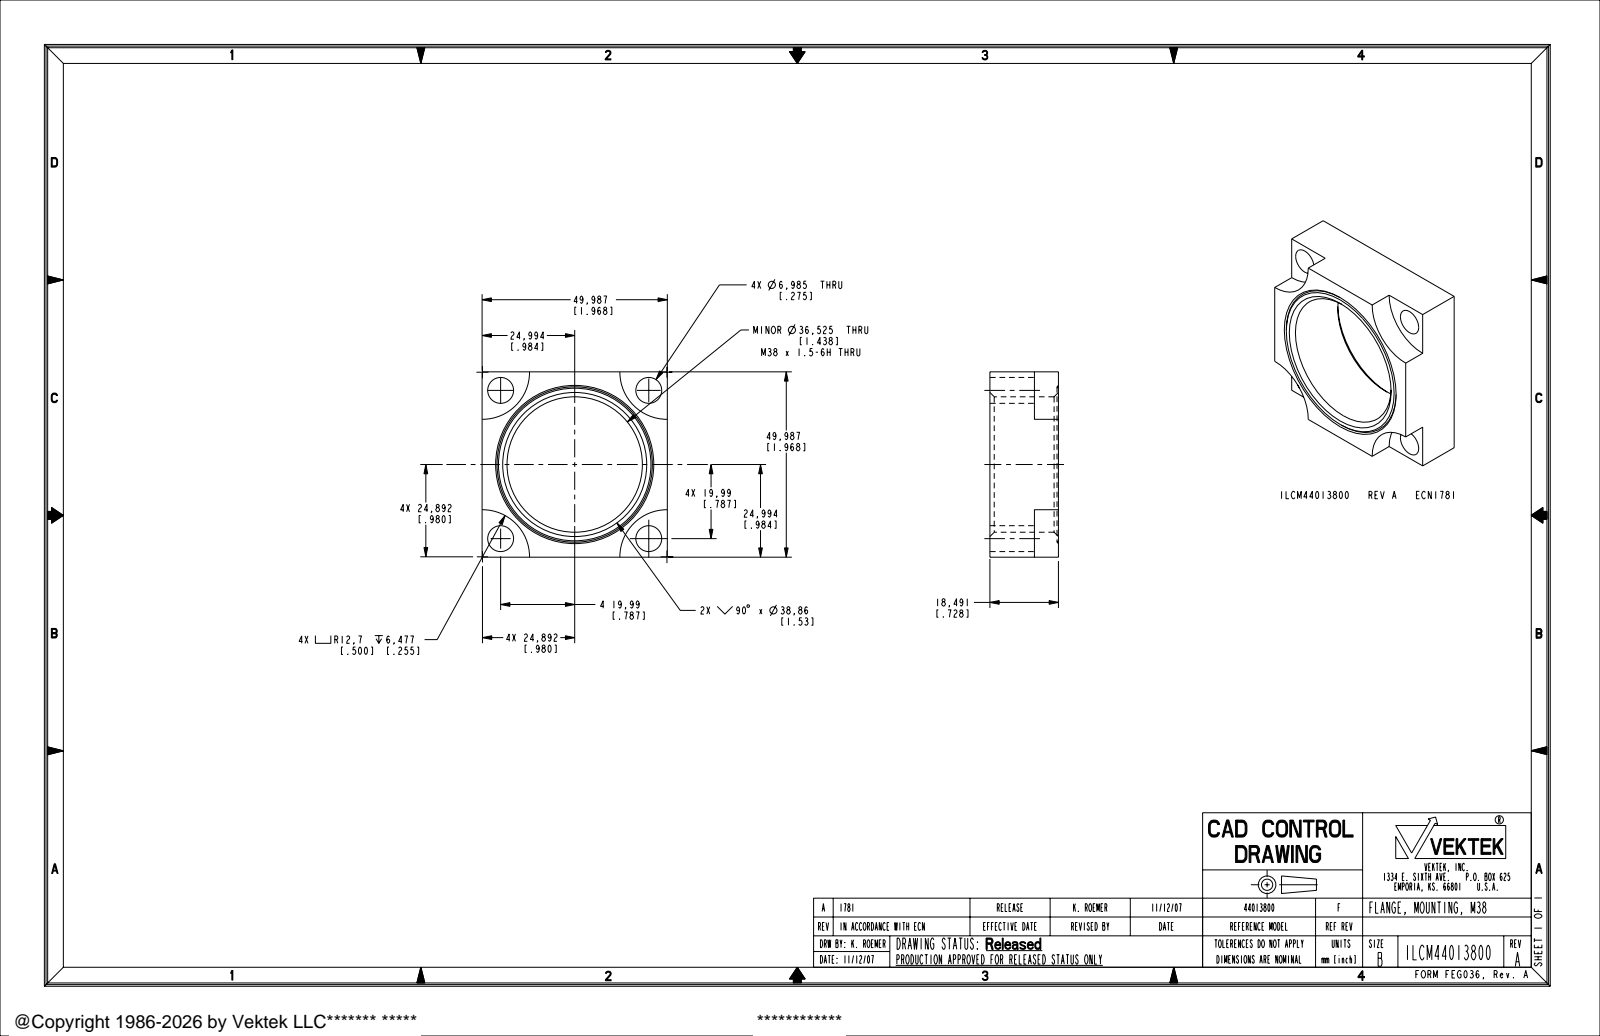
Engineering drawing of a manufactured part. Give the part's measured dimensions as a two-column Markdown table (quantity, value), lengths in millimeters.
| quantity | value |
| --- | --- |
| part name | ILCM44013800 |
| STEP written by | PRO/ENGINEER BY PARAMETRIC TECHNOLOGY CORPORATION, 2005180 (AUTOMOTIVE_DESIGN_CC2) |
| units | millimeters |
| bodies | 1 solid, 33 faces (11 planar, 14 cylindrical, 8 other) |
| overall size | 49.99 × 49.99 × 18.49 |
| volume | 21 460 mm³ |
| surface area | 9 216 mm² |
| round holes (diameter × count) | 6.99 × 4, 36.52 × 1 |
| partial cylindrical surfaces (radius × count) | 12.7 × 4 |
| main face-to-face distances | 49.98, 18.49, 6.48, 12.01 |
| hole center spacings | 28.27, 39.98, 56.54 |
